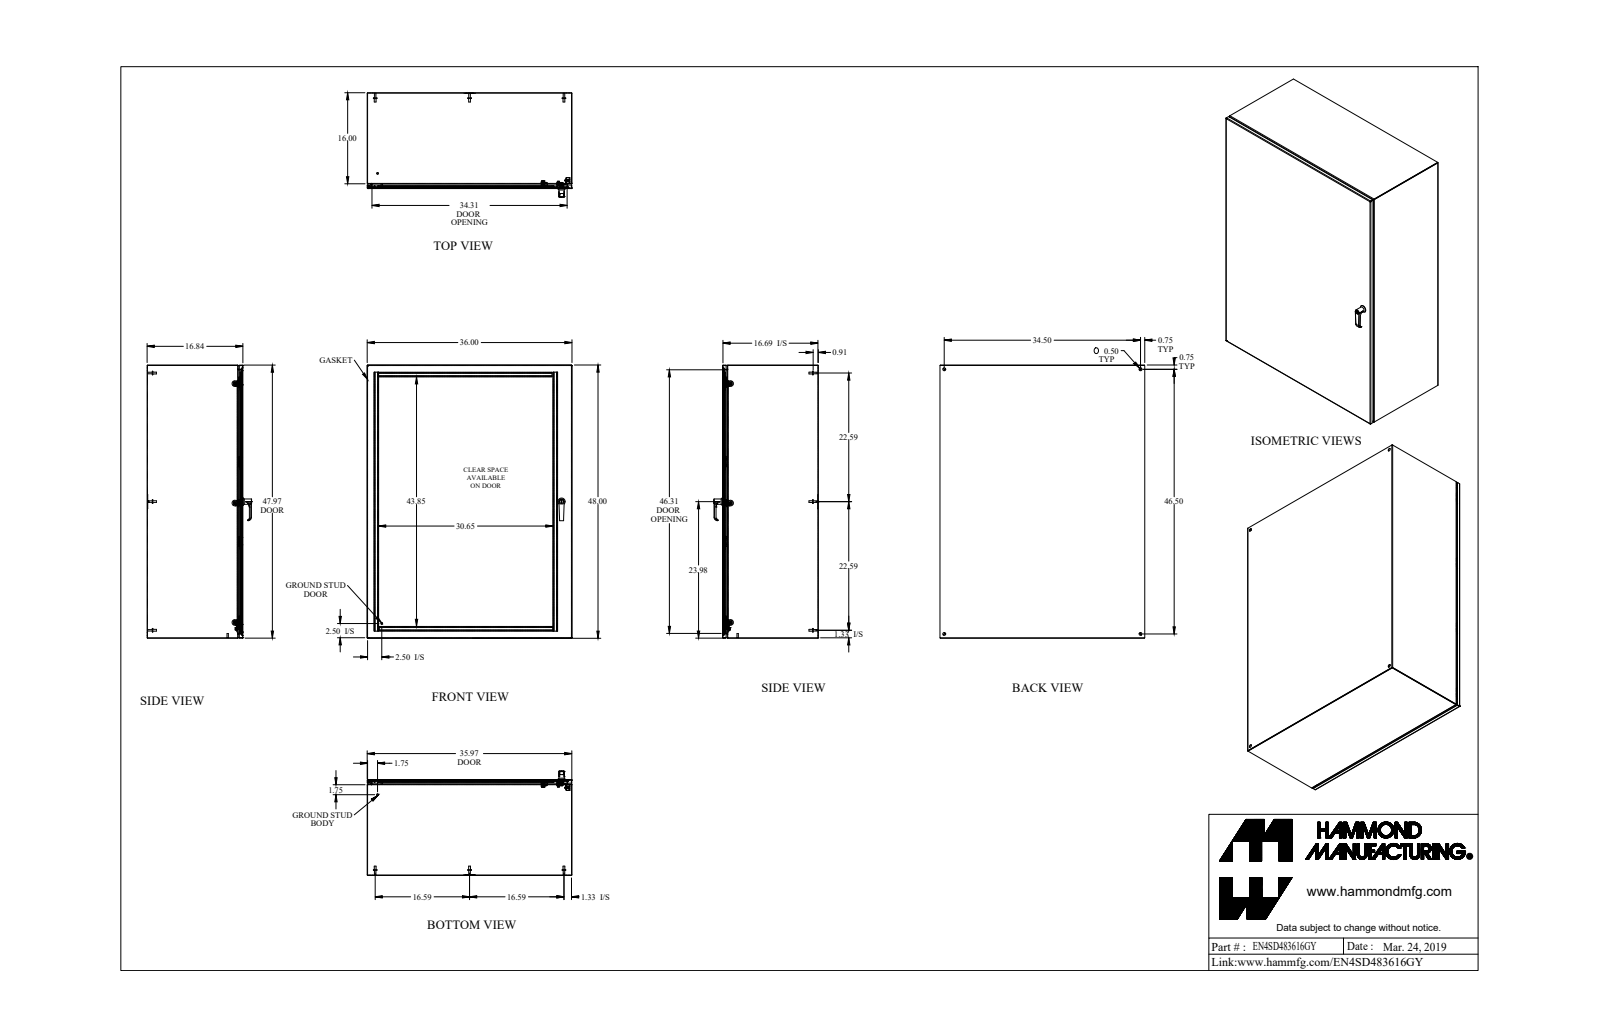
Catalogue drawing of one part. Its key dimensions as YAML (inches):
part_name: "EN4SD483616GY"
step_written_by: "SolidWorks 2018 (AUTOMOTIVE_DESIGN)"
units: inches
bodies: {solids: 63, faces: 1719, planar: 757, cylindrical: 632, other: 330}
overall_size: [48, 36, 18.367]
volume: 502.9
surface_area: 14066
round_holes:
  - {diameter: 0.176, count: 6}
  - {diameter: 0.196, count: 4}
  - {diameter: 0.5, count: 4}
  - {diameter: 0.25, count: 3}
  - {diameter: 0.265, count: 3}
  - {diameter: 0.413, count: 3}
  - {diameter: 0.256, count: 2}
  - {diameter: 0.313, count: 2}
  - {diameter: 0.394, count: 2}
  - {diameter: 0.172, count: 1}
  - {diameter: 0.24, count: 1}
  - {diameter: 0.242, count: 1}
round_bosses_or_shafts:
  - {diameter: 0.313, count: 8}
  - {diameter: 0.27, count: 8}
  - {diameter: 0.25, count: 7}
  - {diameter: 0.625, count: 6}
  - {diameter: 0.375, count: 6}
  - {diameter: 0.156, count: 6}
  - {diameter: 1, count: 3}
  - {diameter: 0.625, count: 3}
partial_cylinders:
  - {radius: 0.043, count: 24}
  - {radius: 0.081, count: 24}
  - {radius: 0.036, count: 18}
  - {radius: 0.108, count: 18}
  - {radius: 0.062, count: 17}
  - {radius: 0.03, count: 15}
  - {radius: 0.094, count: 10}
  - {radius: 0.016, count: 9}
face_to_face_distances: [0.072, 16.765, 16.693, 16.837, 35.928, 35.856, 36, 0.072, 47.856, 47.928]
hole_center_spacings: [41.969, 0.787, 20.981, 20.988, 21, 33.504, 34.5, 46.5]
